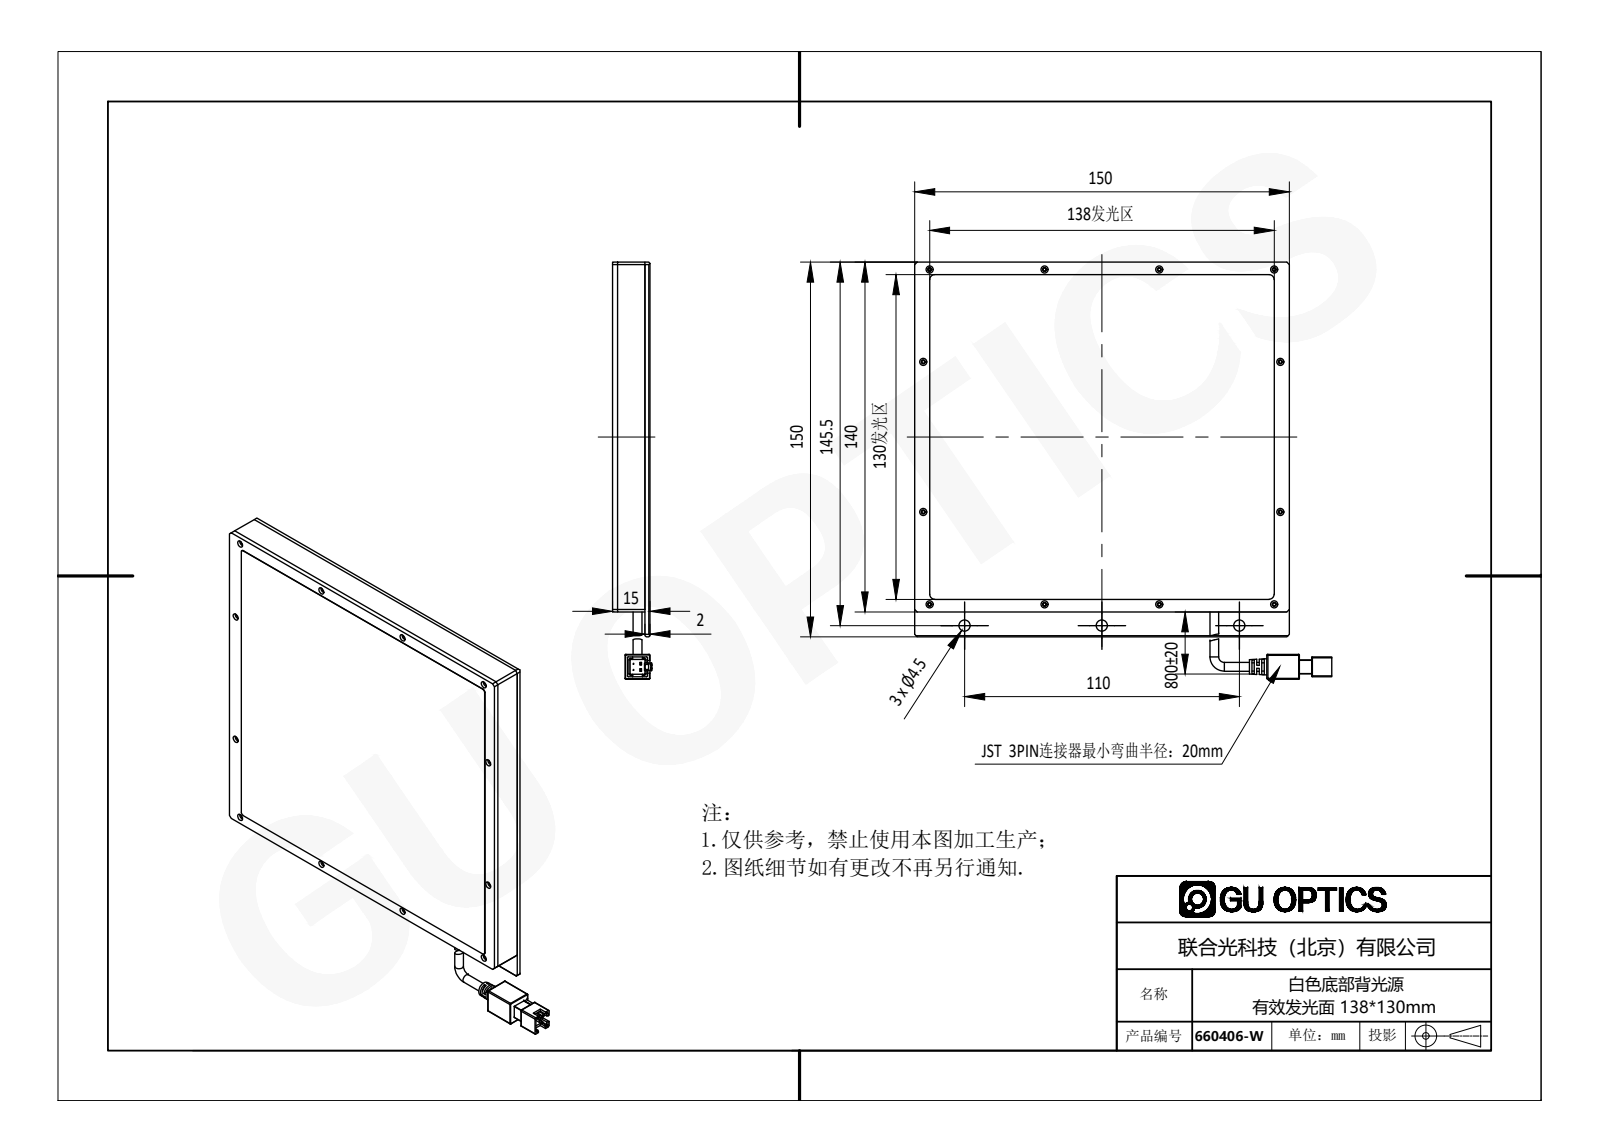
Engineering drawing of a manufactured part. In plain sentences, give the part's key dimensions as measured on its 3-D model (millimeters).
The part is named "660406-W". Its 3-D file was written by "SolidWorks 2016 (AUTOMOTIVE_DESIGN)". It is 22 solids with 3021 faces: 2610 planar, 253 cylindrical and 158 other. Overall it measures 167 by 167 by 15.9 millimeters. Its volume is 165 313 cubic millimeters and its surface area 154 286 square millimeters. Round holes: 12 of diameter 1.1, 12 of diameter 1.4, 12 of diameter 1.5, 12 of diameter 1.6, 12 of diameter 2, 12 of diameter 2.2, 12 of diameter 2.8, 3 of diameter 4.5. Round bosses or shafts: 2 of diameter 3.5. Partial cylindrical surfaces (rounded edges, fillets, slot ends): 15 of radius 0.1, 13 of radius 0.2, 12 of radius 0.4, 6 of radius 1, 4 of radius 2, 2 of radius 1.5, 1 of radius 0.3, 1 of radius 0.68. The main face-to-face distances are 2, 11, 13, 15.2, 13.2, 2.2, 4, 9, 11.2, 5. The hole center spacings are 46, 141.68, 37.08, 61, 92, 97.03, 101.49, 108.45.
